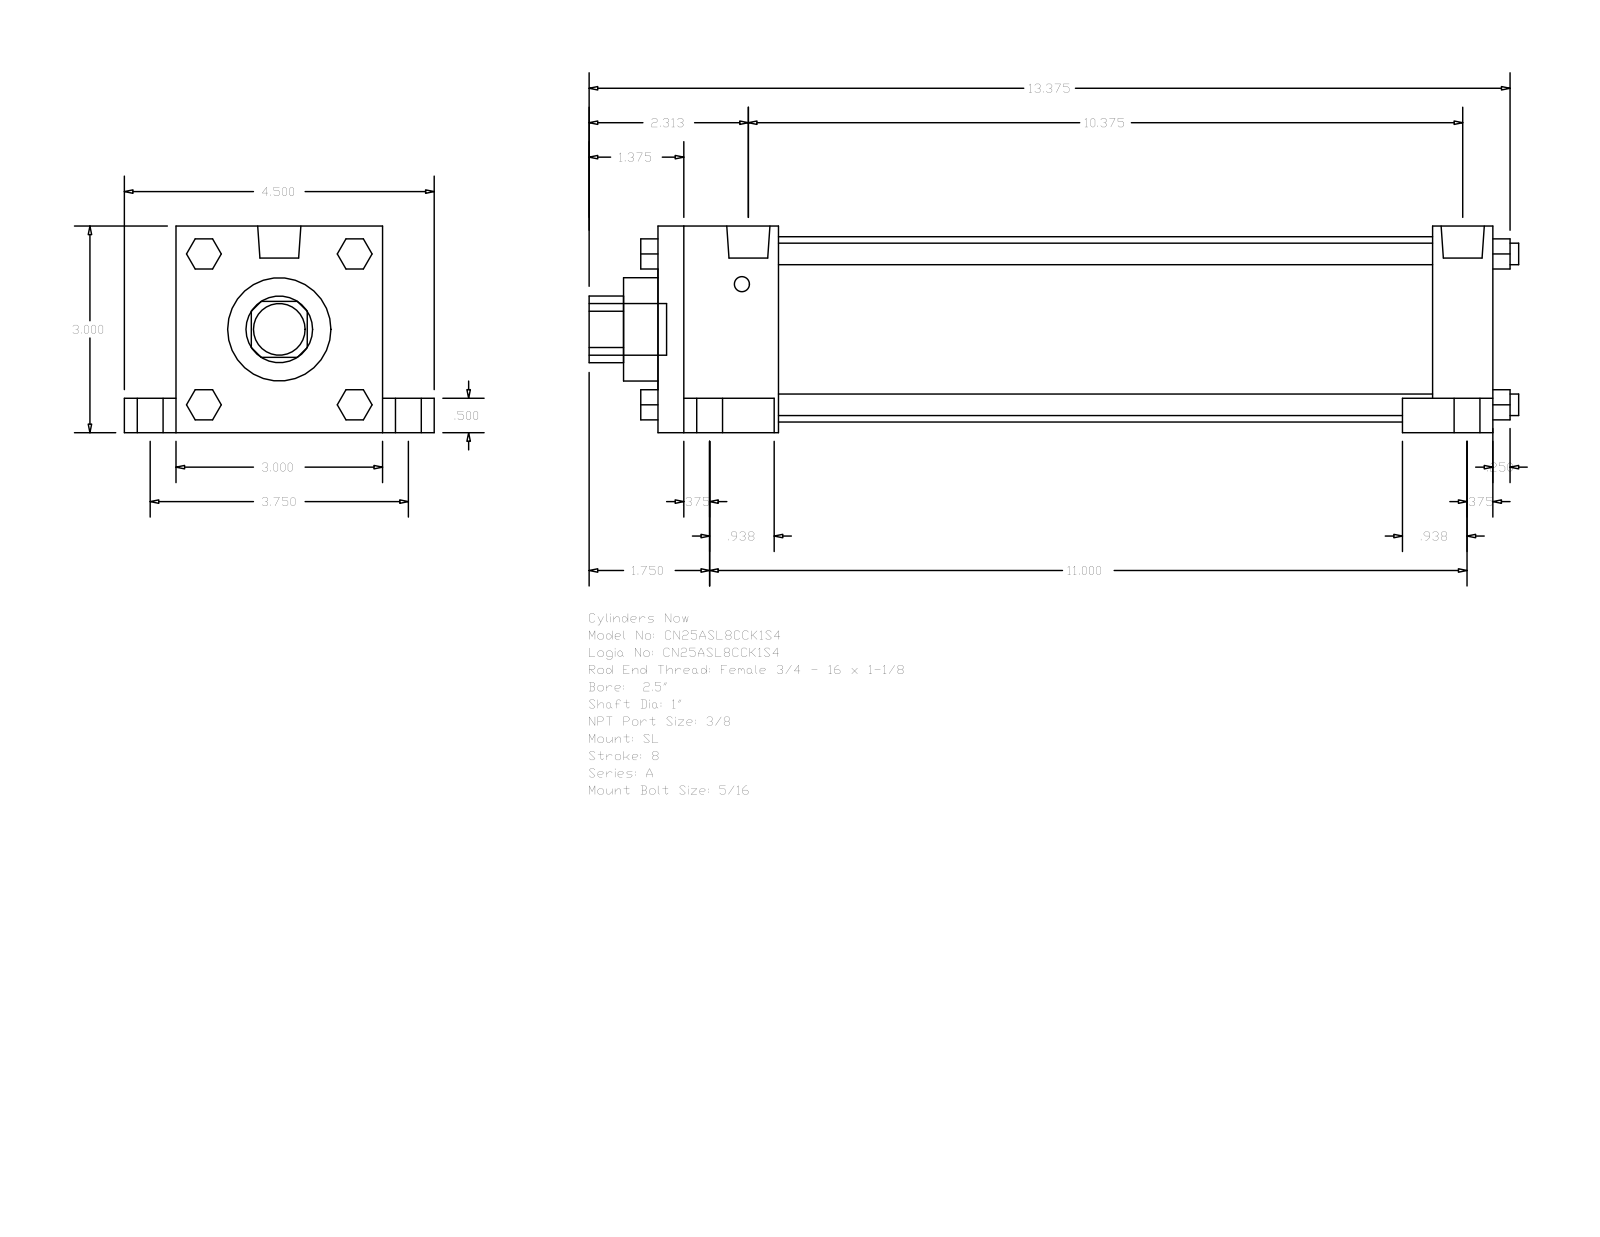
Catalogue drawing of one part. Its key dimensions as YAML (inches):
part_name: "A_SL__0250_1"
step_written_by: "GSSL Pune (CONFIG_CONTROL_DESIGN)"
units: inches
bodies: {solids: 0, faces: 148, planar: 112, cylindrical: 36, other: 0}
overall_size: [13.5, 4.5, 3]
round_holes:
  - {diameter: 1, count: 1}
  - {diameter: 1.5, count: 1}
  - {diameter: 2.69, count: 1}
round_bosses_or_shafts:
  - {diameter: 0.625, count: 4}
  - {diameter: 0.375, count: 4}
  - {diameter: 0.313, count: 4}
  - {diameter: 0.219, count: 4}
  - {diameter: 0.627, count: 2}
  - {diameter: 0.75, count: 1}
partial_cylinders:
  - {radius: 0.484, count: 1}
face_to_face_distances: [3, 12.125, 0.5, 1.75, 10.375, 11.25, 9.5, 0.875, 0.75, 2.5]
